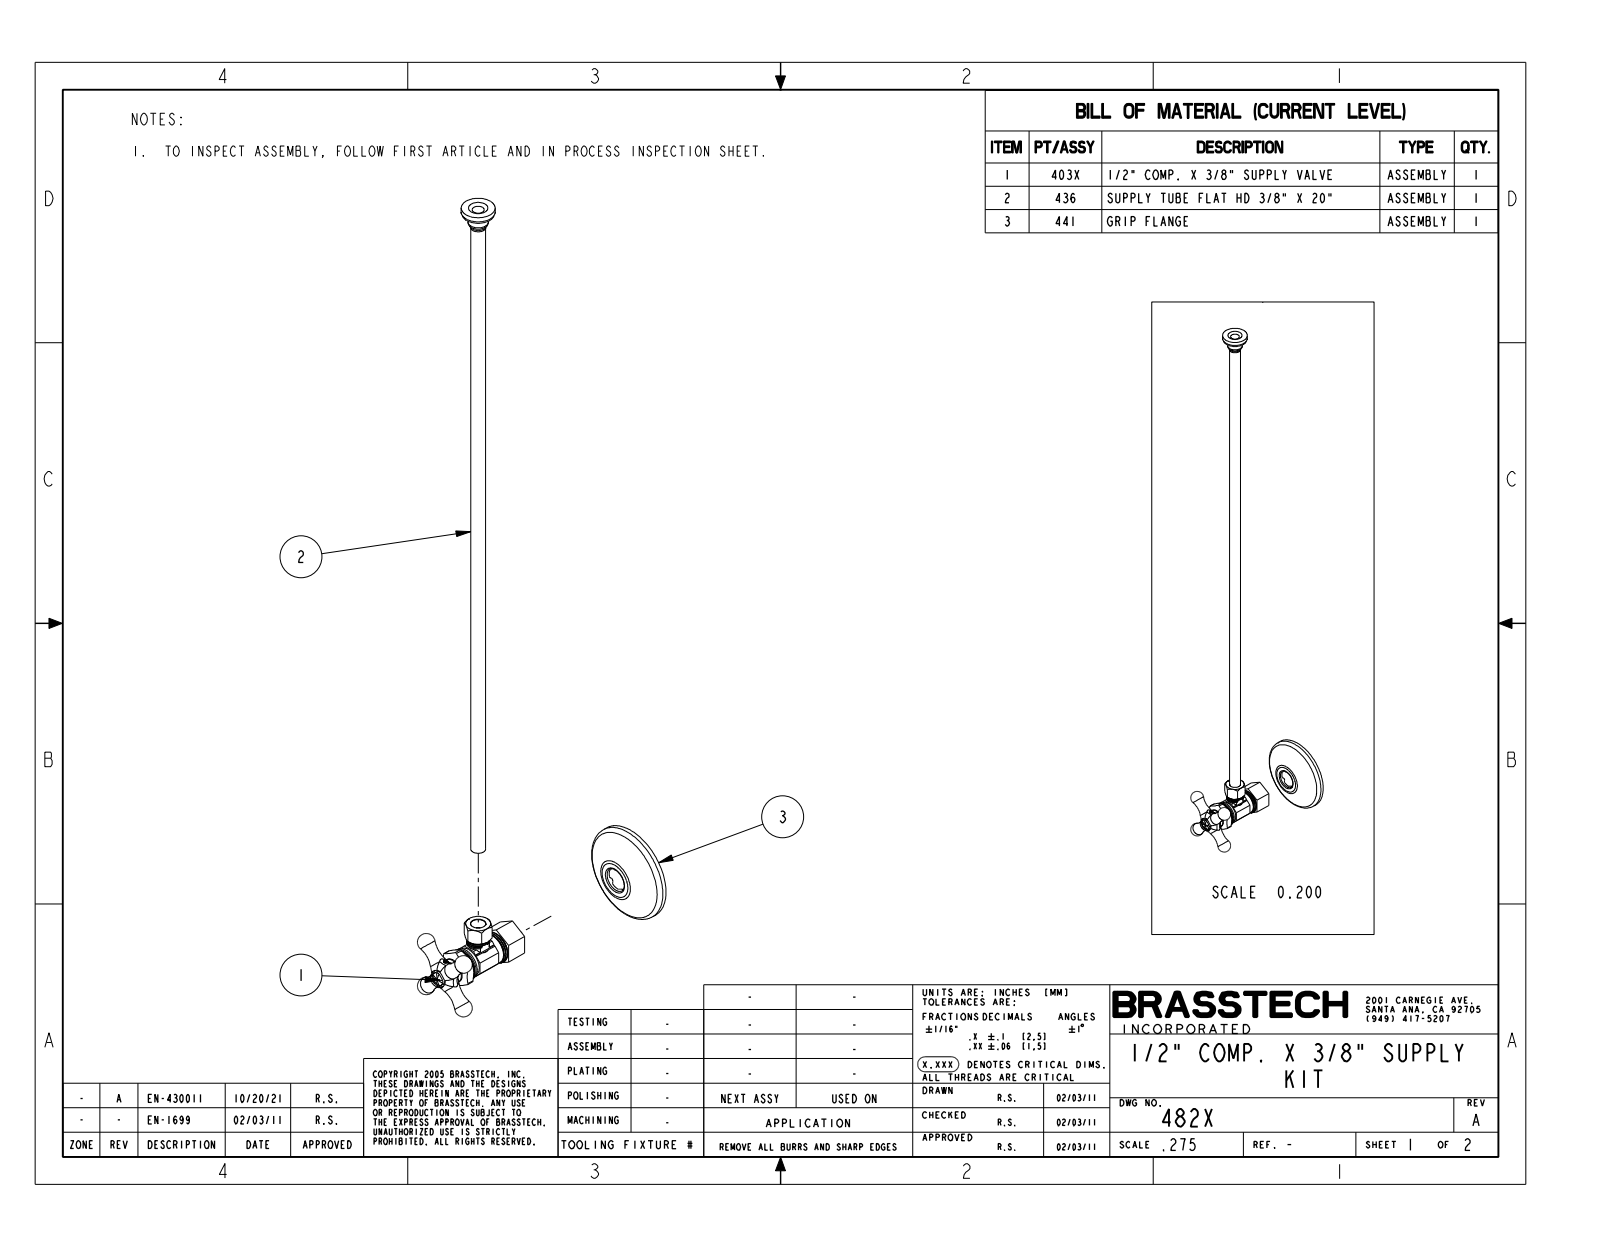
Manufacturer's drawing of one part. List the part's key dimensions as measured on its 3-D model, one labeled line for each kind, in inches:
Part name (STEP PRODUCT): 482X
STEP written by: CREO PARAMETRIC BY PTC INC, 2018500 (CONFIG_CONTROL_DESIGN)
Units: inches
Bodies: 1 solid, 816 faces (268 planar, 238 cylindrical, 310 other)
Overall size (bounding box): 21.155 × 4.431 × 2.5
Volume: 2.16 in³ · Surface area: 119.1 in²
Round holes (diameter × count): ⌀0.13 ×1, ⌀0.25 ×1, ⌀0.335 ×1, ⌀0.375 ×1, ⌀0.38 ×1, ⌀0.39 ×1, ⌀0.392 ×1, ⌀0.4 ×1, ⌀0.464 ×1, ⌀0.48 ×1, ⌀0.563 ×1, ⌀0.62 ×1
Round bosses / shafts (diameter × count): ⌀2.5 ×1, ⌀0.86 ×1, ⌀0.845 ×1, ⌀0.8 ×1, ⌀0.68 ×1, ⌀0.677 ×1, ⌀0.665 ×1, ⌀0.629 ×1
Partial cylindrical surfaces — rounded edges, fillets, slot ends (radius × count): R0.01 ×18, R0.03 ×10, R0.05 ×6, R0.058 ×5, R0.082 ×1, R0.17 ×1, R0.376 ×1, R0.444 ×1
Main face-to-face distances: 0.875, 0.625, 0.8, 0.563, 0.125, 0.75, 1.813, 0.459, 0.103, 0.037
Hole centre spacings: 1.09
